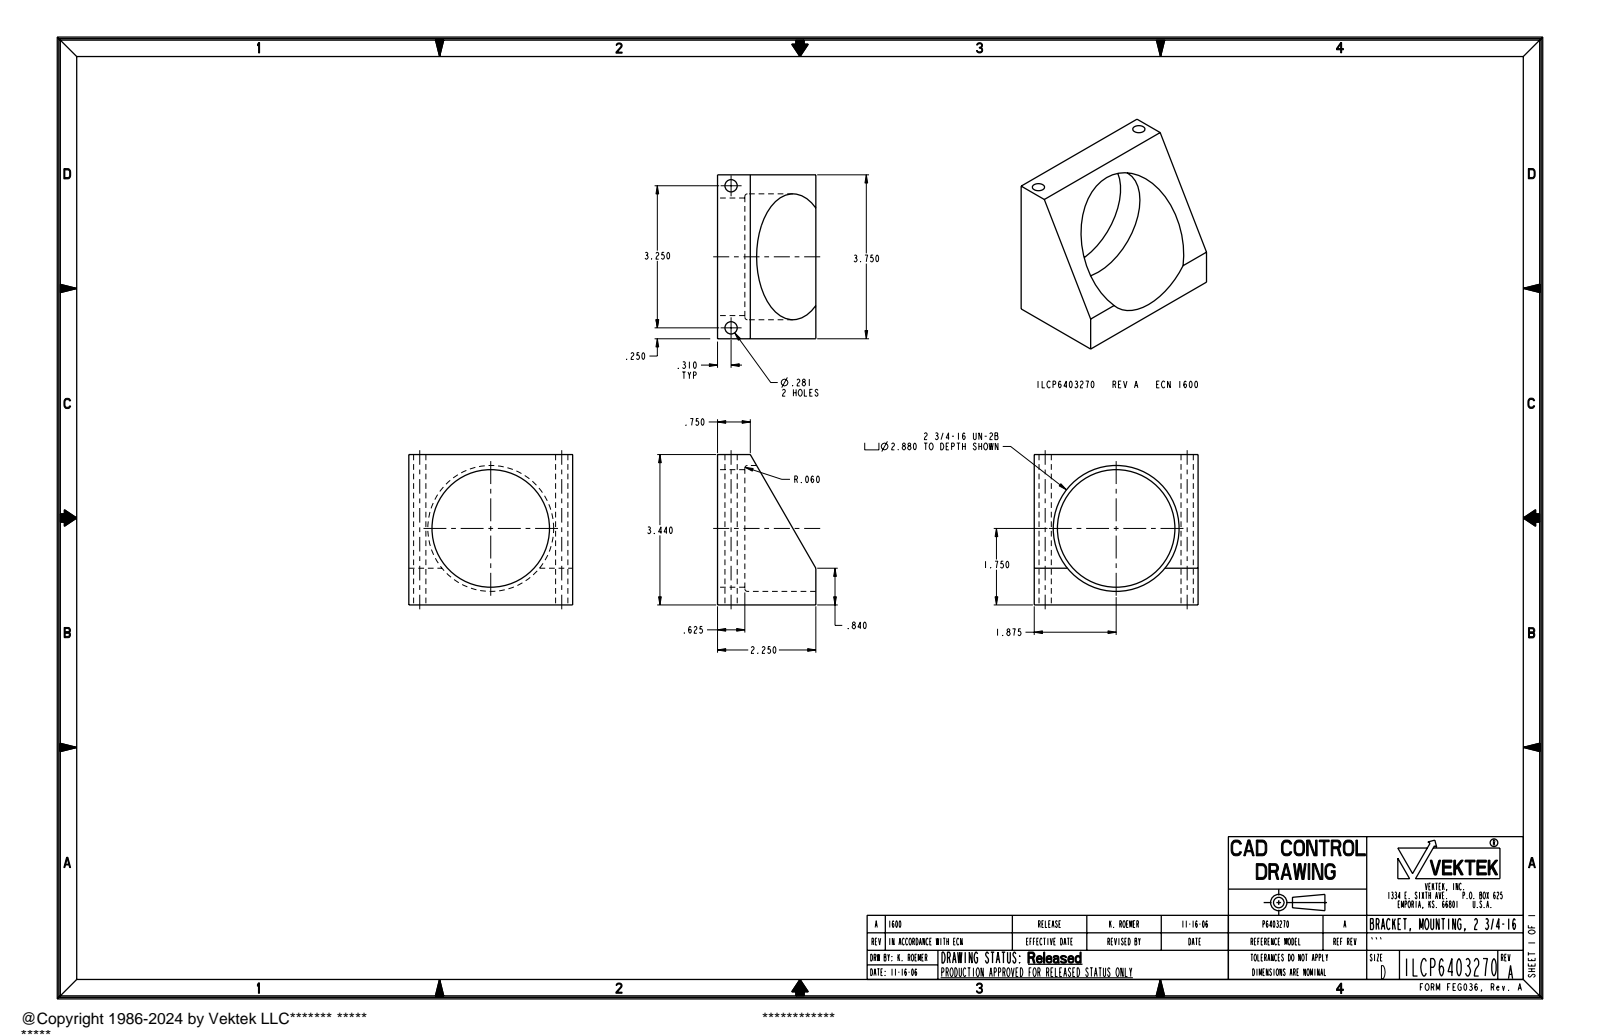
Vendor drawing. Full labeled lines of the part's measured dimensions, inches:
Part name (STEP PRODUCT): ILCP6403270
STEP written by: PRO/ENGINEER BY PARAMETRIC TECHNOLOGY CORPORATION, 2005180 (AUTOMOTIVE_DESIGN_CC2)
Units: inches
Bodies: 1 solid, 18 faces (8 planar, 8 cylindrical, 2 other)
Overall size (bounding box): 3.75 × 3.44 × 2.25
Volume: 10.68 in³ · Surface area: 58.21 in²
Round holes (diameter × count): ⌀0.281 ×2, ⌀2.689 ×1, ⌀2.88 ×1
Main face-to-face distances: 3.75, 3.44, 2.25, 1.625, 0.625
Hole centre spacings: 3.25
